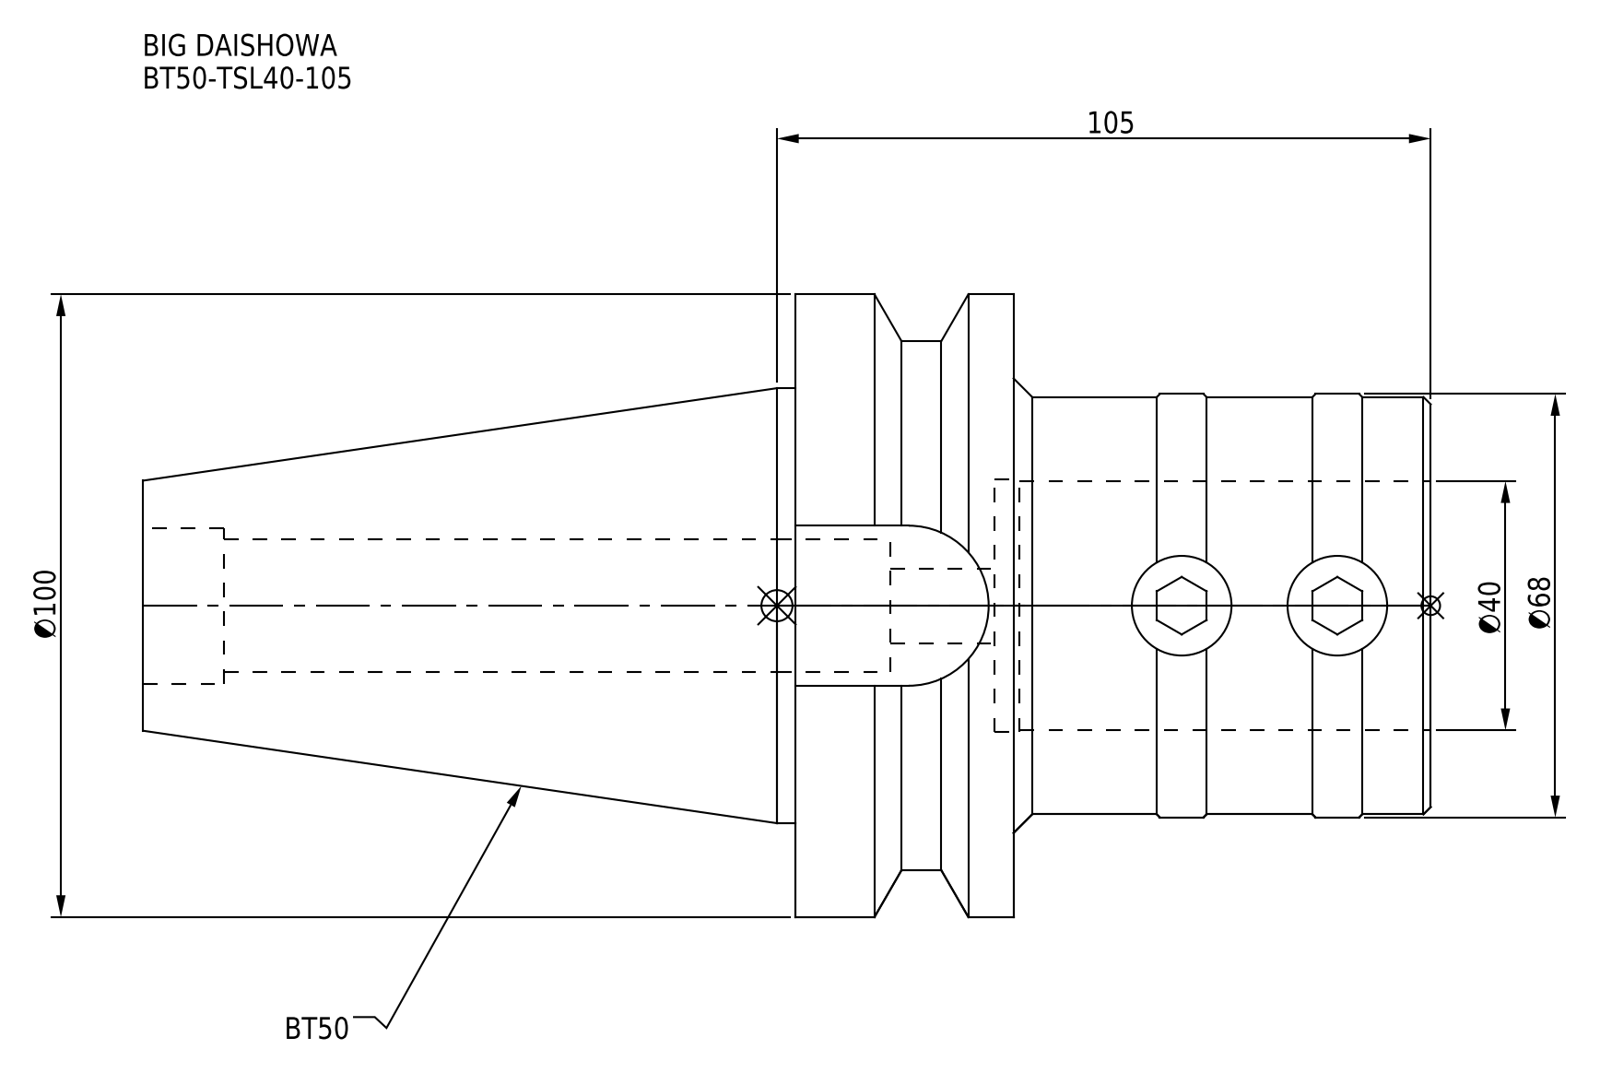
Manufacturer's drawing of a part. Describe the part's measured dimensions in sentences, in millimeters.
The part is named "BT50-TSL40-105". Its 3-D file was written by "CREO PARAMETRIC BY PTC INC, 2016380 (AUTOMOTIVE_DESIGN)". It is 1 solid with 64 faces: 14 planar, 32 cylindrical and 18 other. Overall it measures 206.8 by 100 by 100 millimeters. Its volume is 598 504 cubic millimeters and its surface area 76 392 square millimeters. Round holes: 1 of diameter 12, 1 of diameter 21.2, 1 of diameter 25, 1 of diameter 40, 1 of diameter 40.6. Round bosses or shafts: 1 of diameter 100, 1 of diameter 85, 1 of diameter 69.85, 1 of diameter 68, 1 of diameter 67. Partial cylindrical surfaces (rounded edges, fillets, slot ends): 1 of radius 12.85. The main face-to-face distances are 35, 67, 102, 70, 3, 32, 206.8, 139.8, 136.8, 104.8.
